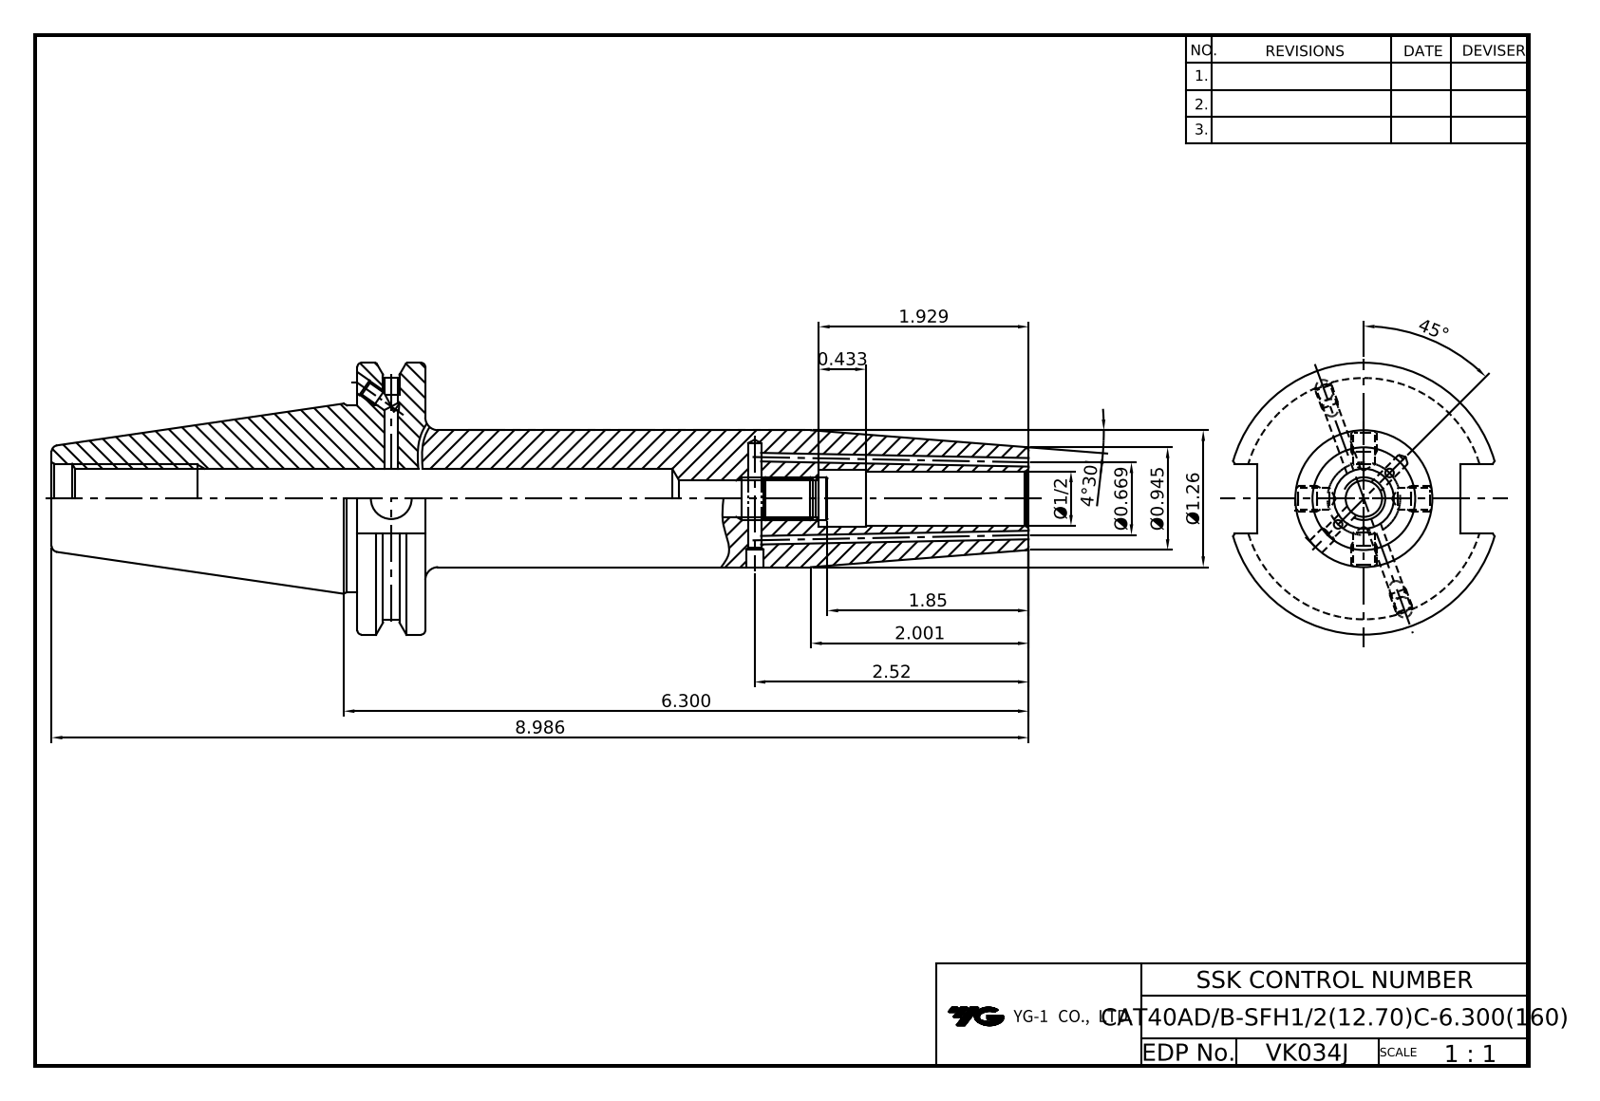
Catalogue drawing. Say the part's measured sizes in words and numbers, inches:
The part is named "LO-CAT40ADB-SFH12.7C-160". Its 3-D file was written by "Autodesk Inventor 2024 (AUTOMOTIVE_DESIGN)". It is 1 solid with 92 faces: 39 planar, 31 cylindrical and 22 other. Overall it measures 8.986 by 2.5 by 2.405 inches. Its volume is 11.41 cubic inches and its surface area 62.15 square inches. Round holes: 4 of diameter 0.128, 2 of diameter 0.098, 2 of diameter 0.157, 2 of diameter 0.165, 1 of diameter 0.351, 1 of diameter 0.375, 1 of diameter 0.5, 1 of diameter 0.512, 1 of diameter 0.527, 1 of diameter 0.547, 1 of diameter 0.642. Round bosses or shafts: 1 of diameter 2.5, 1 of diameter 1.717, 1 of diameter 1.26. Partial cylindrical surfaces (rounded edges, fillets, slot ends): 1 of radius 1.108. The main face-to-face distances are 0.625, 6.174, 5.549, 1.874, 0.645, 2.812, 3.437, 8.986, 3.05, 0.238.
